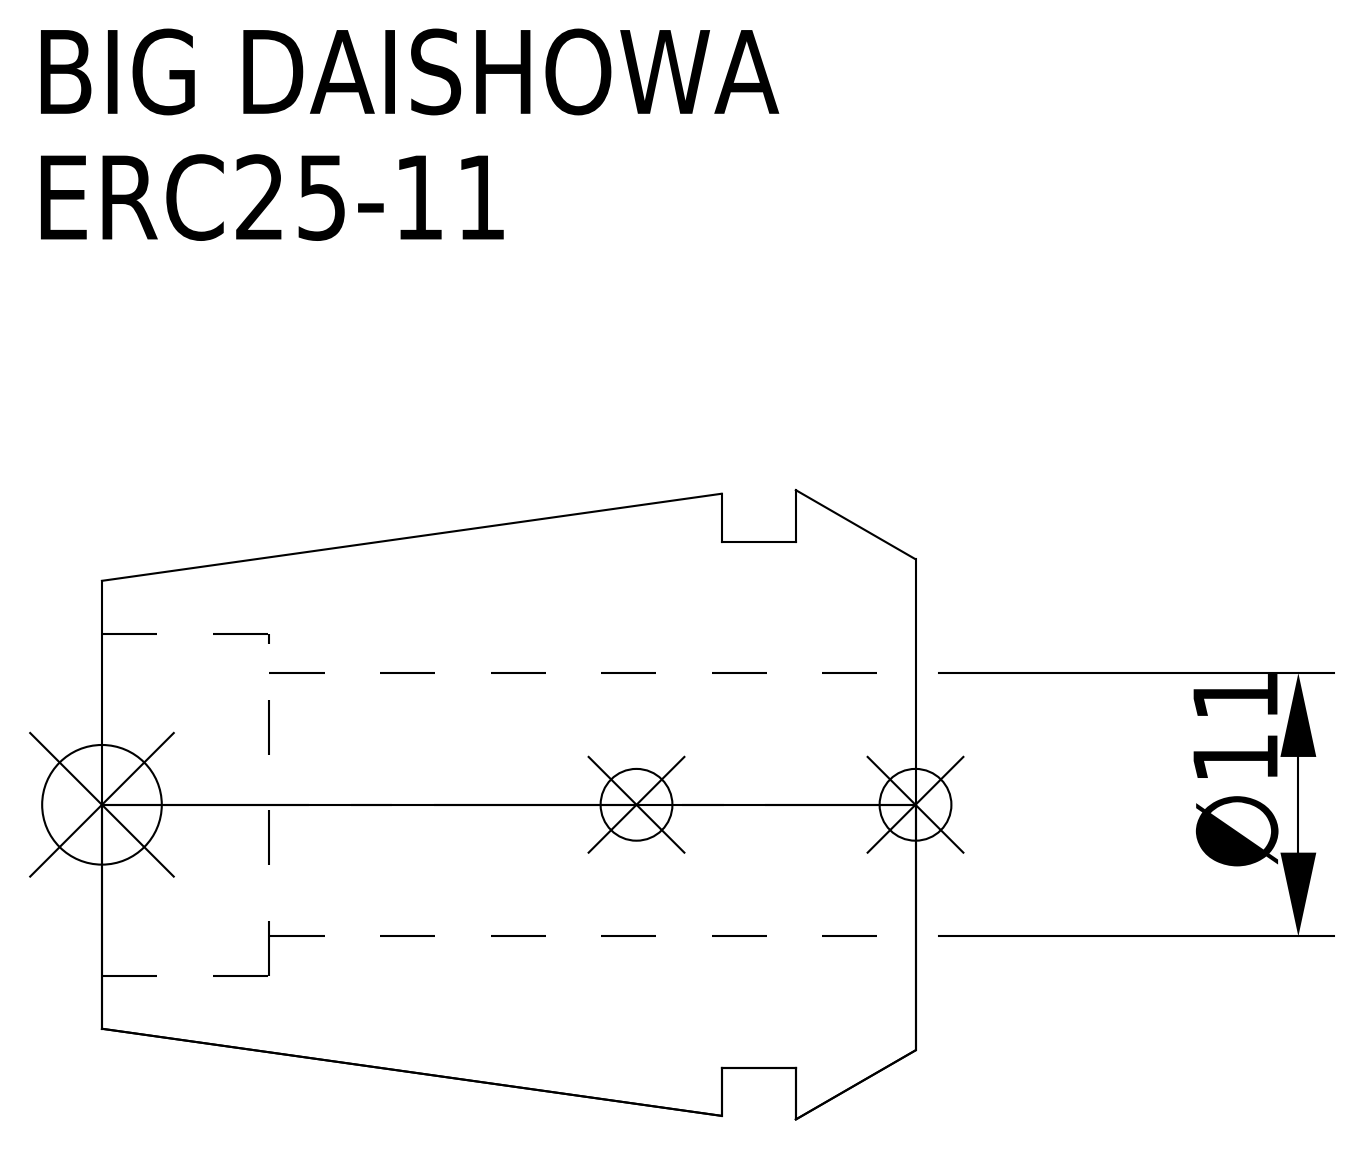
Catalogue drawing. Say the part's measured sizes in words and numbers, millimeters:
The part is named "ERC25-11". Its 3-D file was written by "CREO PARAMETRIC BY PTC INC, 2016380 (AUTOMOTIVE_DESIGN)". It is 1 solid with 15 faces: 5 planar, 6 cylindrical and 4 other. Overall it measures 34 by 26.3 by 26.3 millimeters. Its volume is 9 913 cubic millimeters and its surface area 4 454 square millimeters. Round holes: 1 of diameter 11, 1 of diameter 14.3. Round bosses or shafts: 1 of diameter 22. The main face-to-face distances are 5, 8.1, 3.1, 34, 29, 25.9, 27, 22, 18.9, 7.
